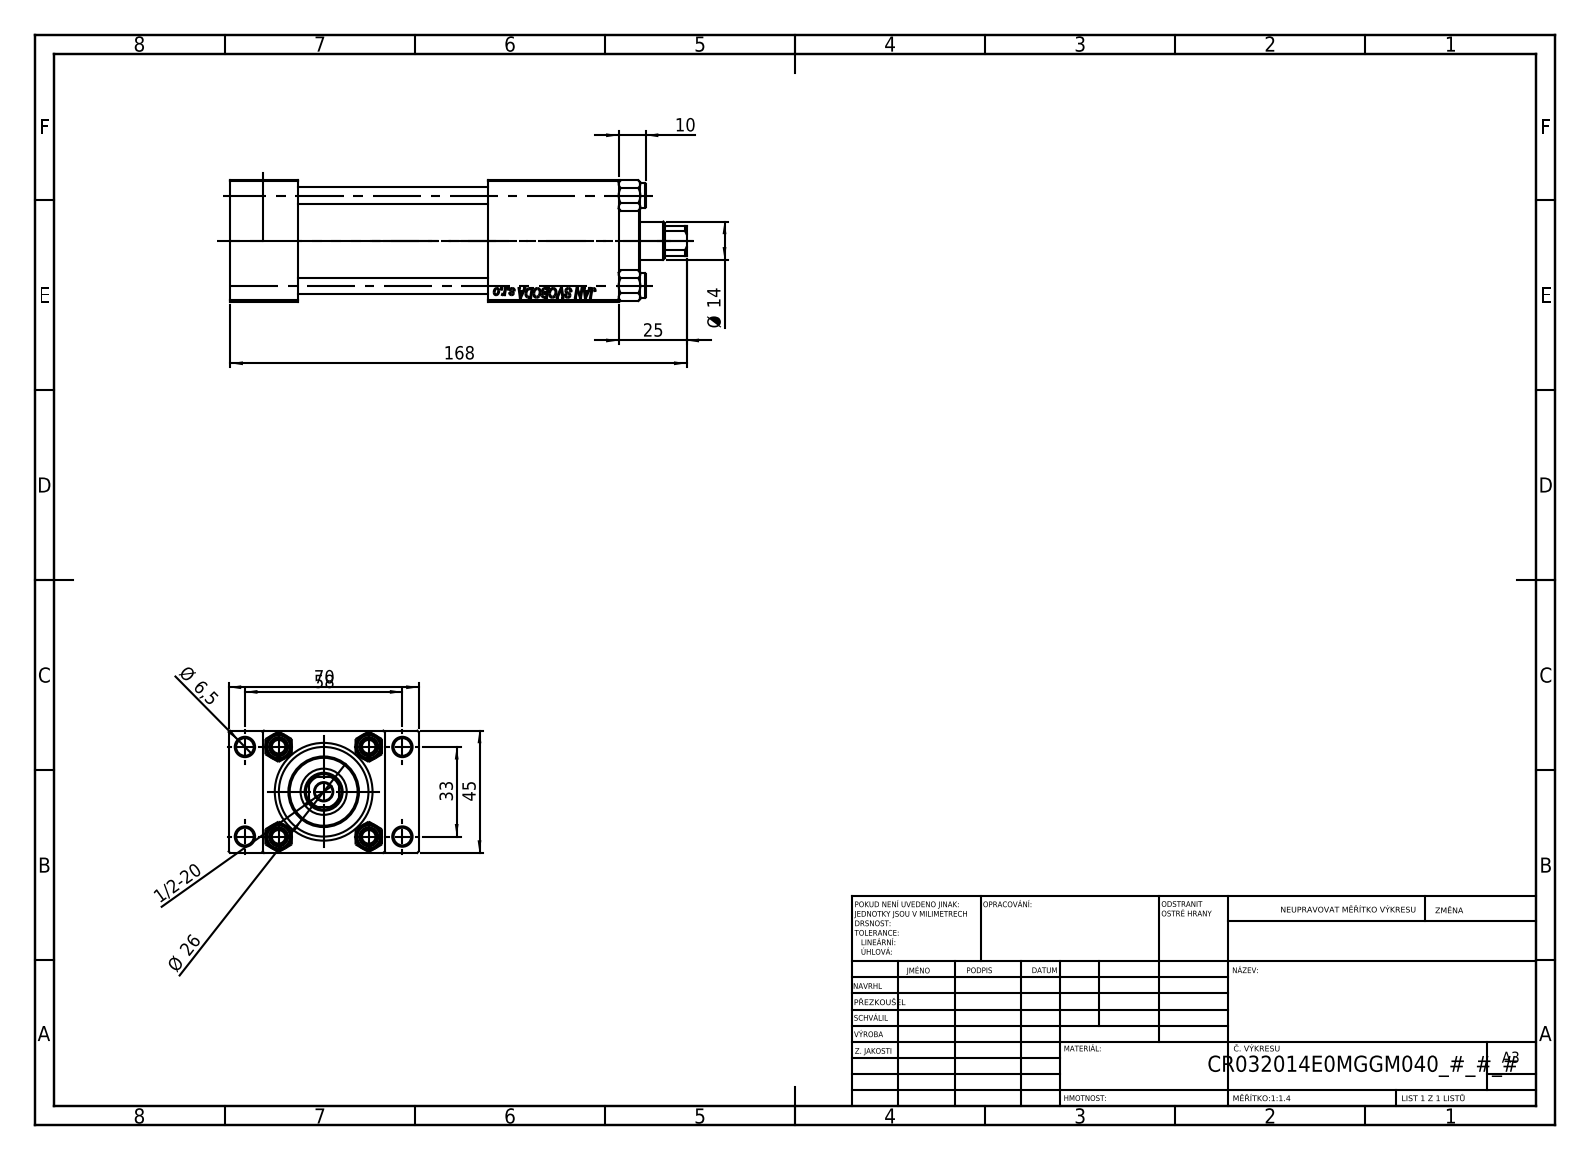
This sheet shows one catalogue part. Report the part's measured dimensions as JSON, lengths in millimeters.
{"part_name": "V215CR_VCP_E; V215CR_E_Body; NUT_M5_E; V215CR_TYCINKA_E (+1 more)", "step_written_by": "SolidWorks 2019 (CONFIG_CONTROL_DESIGN)", "units": "millimeters", "bodies": {"solids": 11, "faces": 1136, "planar": 497, "cylindrical": 87, "other": 552}, "overall_size": [168, 70, 45], "volume_mm3": 232011, "surface_area_mm2": 82859, "round_holes": [[6.5, 5], [6, 4], [7, 2], [13.16, 2], [20, 2], [14, 1], [17, 1], [24, 1], [32, 1], [33, 1]], "round_bosses_or_shafts": [[9, 4], [38, 1], [26, 1]], "partial_cylinders_radius": [[6.5, 1]], "face_to_face_distances": [45, 25, 12.5, 57.5, 70, 143, 118, 95, 48, 114.3], "hole_center_spacings": [12.4, 23.48, 33.2, 33.37, 35.35, 45.6, 56.35, 33]}
